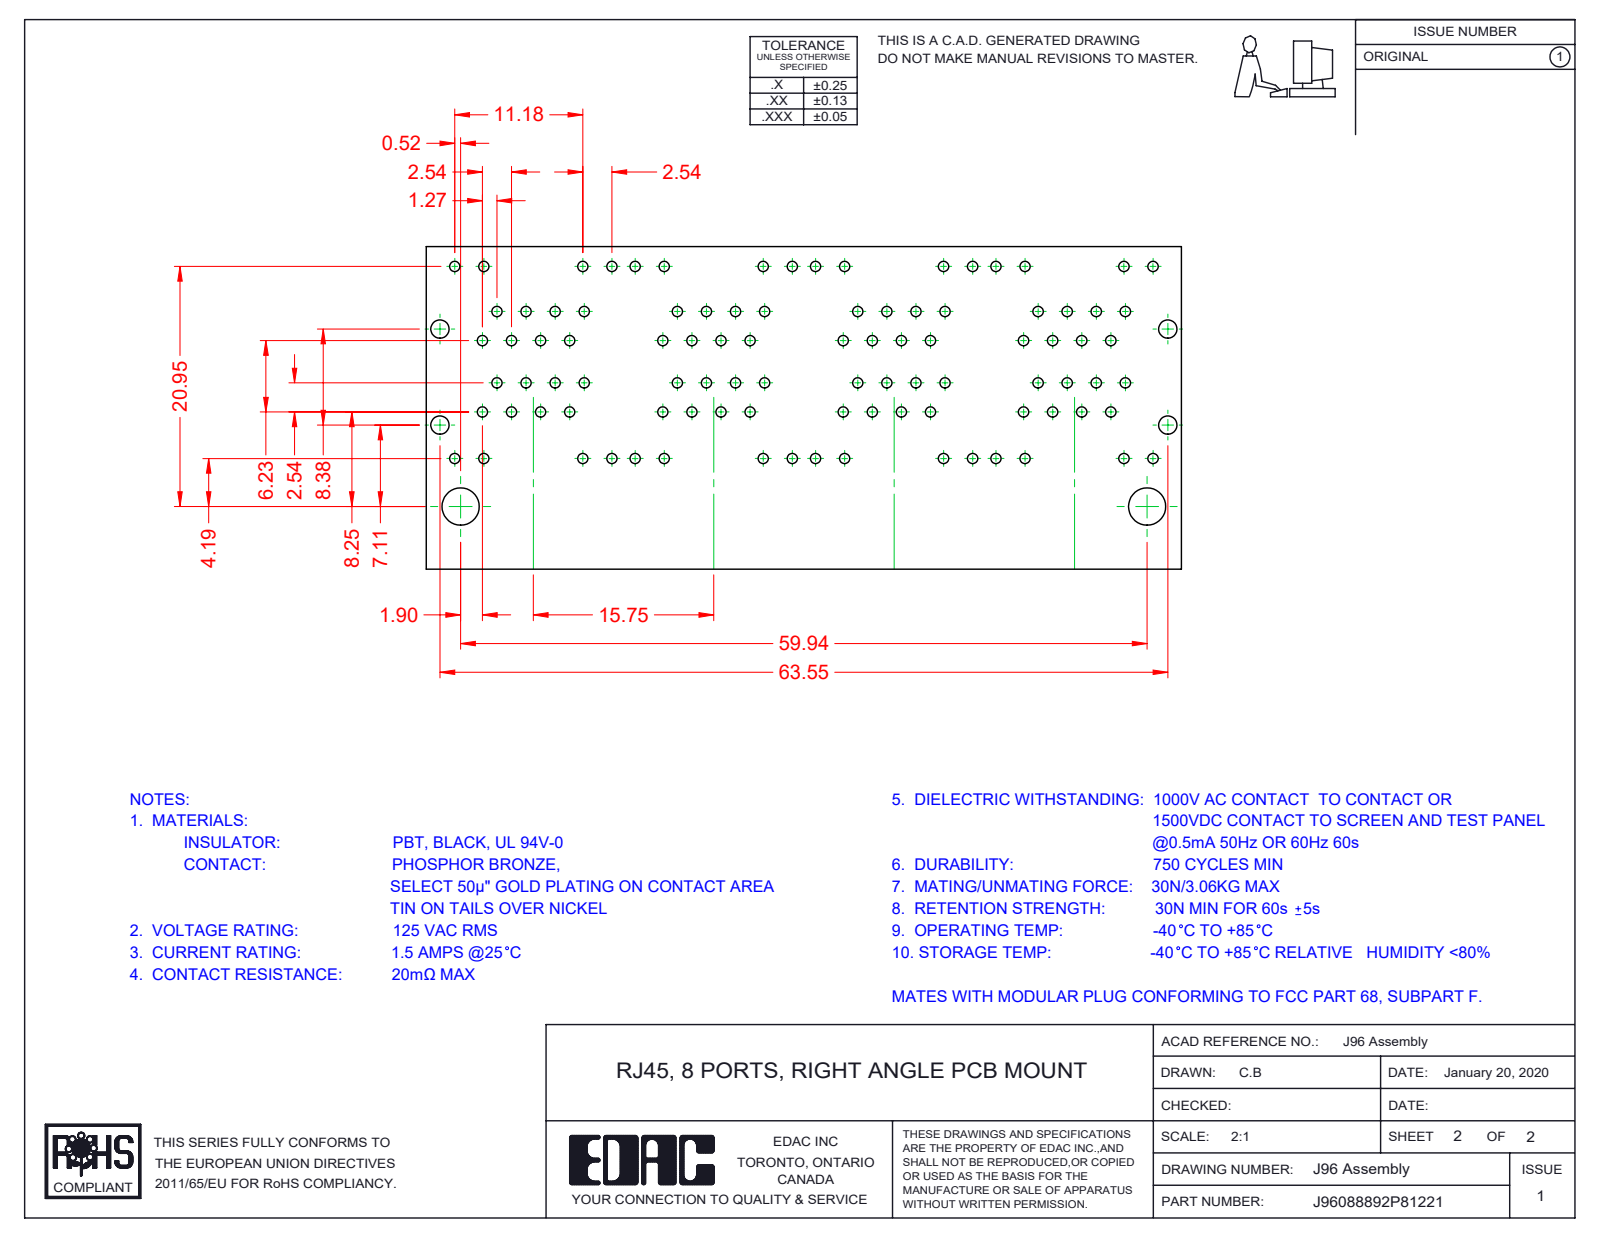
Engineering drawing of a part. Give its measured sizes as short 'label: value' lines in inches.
name: 96 LED LH Lower_8-Red-Yellow; 96 Insulator_8 Ports; 96 Contacts Upper; 96 Contacts Lower (+8 more)
written by: SolidWorks 2016 (CONFIG_CONTROL_DESIGN)
unit: in
bodies: 96 solids, 7820 faces (6105 planar, 1404 cylindrical, 311 other)
size: 2.652 × 1.235 × 1.129
volume: 1.474 in³; area: 98.57 in²
holes: 3× ⌀0.067
bosses: 3× ⌀0.066
rounds: 124× R0.01, 73× R0.014, 72× R0.039, 49× R0.02, 32× R0.036, 27× R0.008, 14× R0.011, 11× R0.028
face distances: 0.62, 0.014, 0.392, 0.046, 0.063, 0.021, 0.393, 0.401, 0.499, 0.133
hole spacings: 0.62, 1.24
